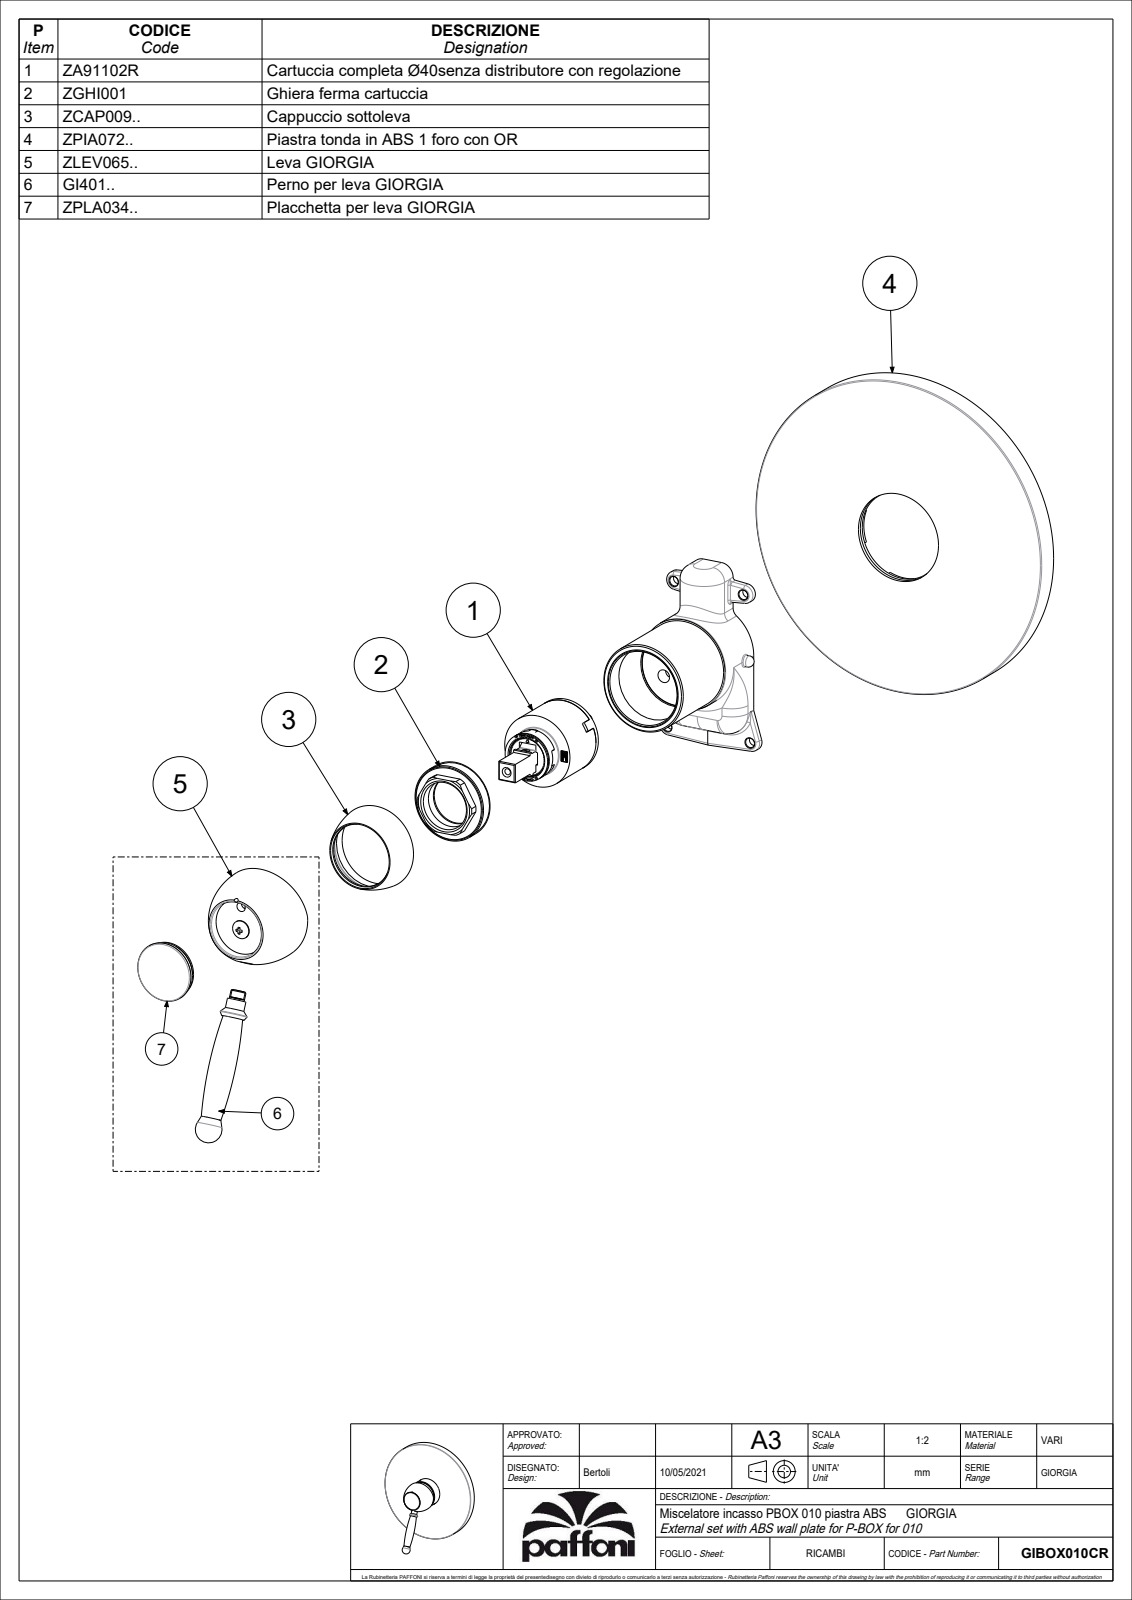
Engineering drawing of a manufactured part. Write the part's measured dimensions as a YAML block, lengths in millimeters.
part_name: "GIBOX010CR"
step_written_by: "CREO PARAMETRIC BY PTC INC, 2020044 (CONFIG_CONTROL_DESIGN)"
units: millimeters
bodies: {solids: 2, faces: 983, planar: 572, cylindrical: 247, other: 164}
overall_size: [177.98, 173, 95.48]
volume: 237900
surface_area: 110798
round_holes:
  - {diameter: 5, count: 3}
  - {diameter: 8, count: 2}
  - {diameter: 3, count: 1}
  - {diameter: 3.3, count: 1}
  - {diameter: 4, count: 1}
  - {diameter: 11, count: 1}
  - {diameter: 12, count: 1}
  - {diameter: 21, count: 1}
  - {diameter: 21.2, count: 1}
  - {diameter: 26.1, count: 1}
  - {diameter: 30.3, count: 1}
  - {diameter: 34.5, count: 1}
round_bosses_or_shafts:
  - {diameter: 173, count: 1}
  - {diameter: 167, count: 1}
  - {diameter: 56.5, count: 1}
  - {diameter: 48.1, count: 1}
  - {diameter: 39.5, count: 1}
  - {diameter: 36.7, count: 1}
  - {diameter: 33, count: 1}
  - {diameter: 32, count: 1}
partial_cylinders:
  - {radius: 0.5, count: 26}
  - {radius: 0.2, count: 24}
  - {radius: 2, count: 1}
  - {radius: 3.5, count: 1}
  - {radius: 7, count: 1}
  - {radius: 10.05, count: 1}
  - {radius: 11.9, count: 1}
  - {radius: 12.3, count: 1}
face_to_face_distances: [13, 11, 2, 2.8, 6.5, 8.2, 10.2, 24.2, 10.1, 21.4]
hole_center_spacings: [8.83, 9.89, 9.9, 14.76, 19.29, 1.6, 1.62, 4.98]
